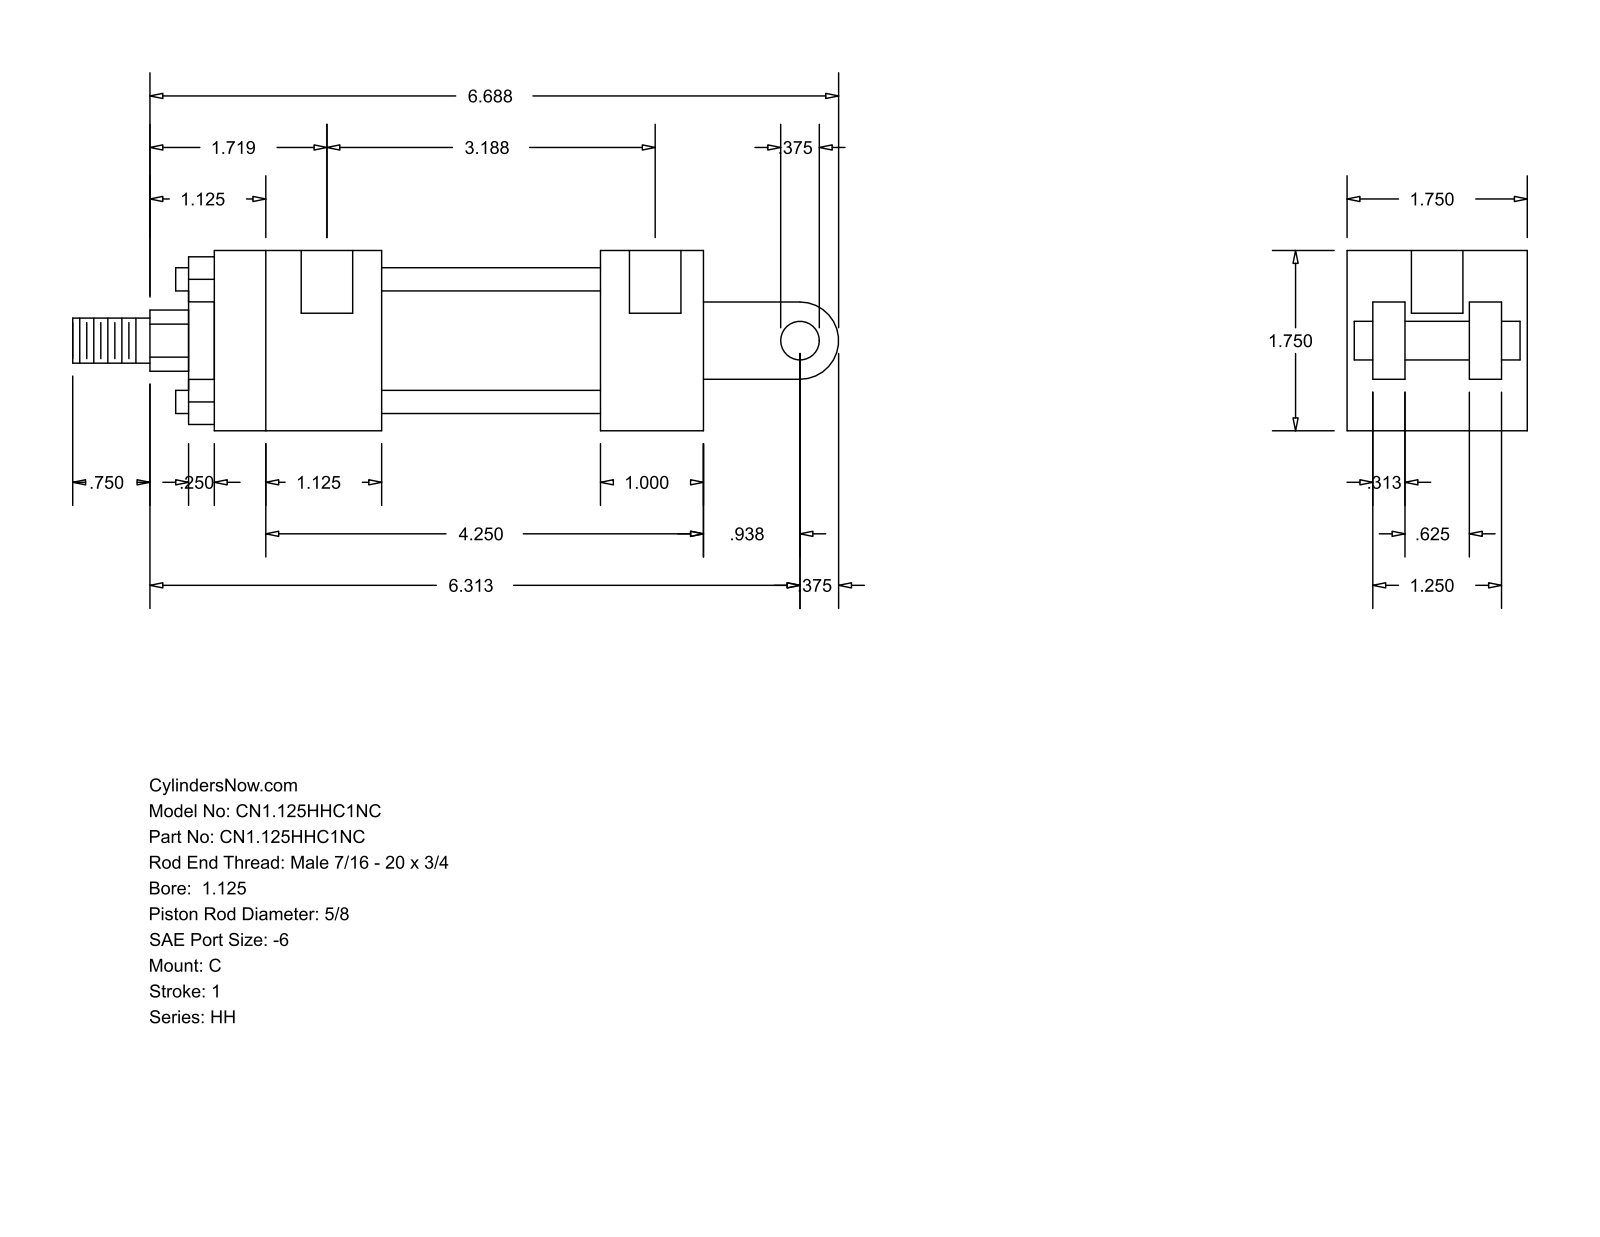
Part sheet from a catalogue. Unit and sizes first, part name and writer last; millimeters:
Units: millimetres
Overall size (bounding box): 188.91 × 44.45 × 44.45
Round holes (diameter × count): ⌀5.56 ×4, ⌀12.7 ×2
Round bosses / shafts (diameter × count): ⌀5.71 ×4, ⌀34.92 ×1, ⌀28.57 ×1, ⌀15.88 ×1, ⌀11.11 ×1, ⌀9.53 ×1
Partial cylindrical surfaces — rounded edges, fillets, slot ends (radius × count): R7.54 ×1, R9.53 ×1
Main face-to-face distances: 44.46, 6.35, 31.76, 14.29, 30.17, 38.11, 7.94, 23.82, 41.27, 12.7
Hole centre spacings: 77.79, 3.17, 80.96
Bodies: 0 solids, 99 faces (70 planar, 29 cylindrical, 0 other)
Part name (STEP PRODUCT): HH_C__0112_0.625
STEP written by: GSSL Pune (CONFIG_CONTROL_DESIGN)
